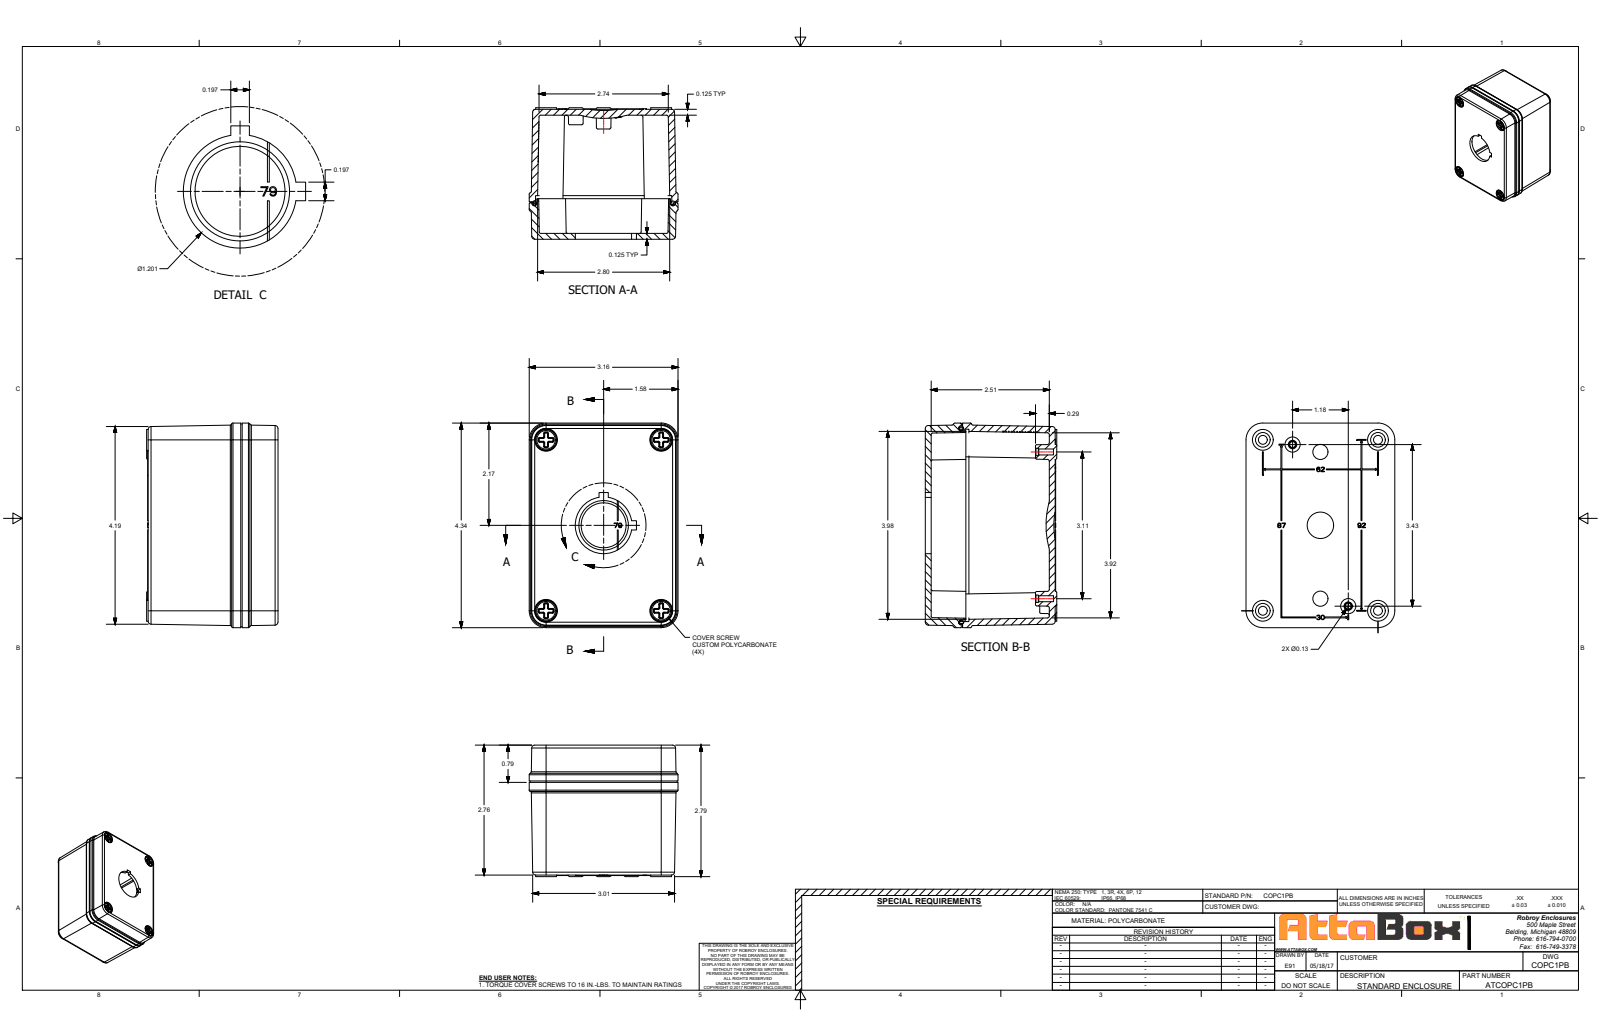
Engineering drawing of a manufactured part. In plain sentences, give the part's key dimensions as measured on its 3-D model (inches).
The part is named "COPC1PB". Its 3-D file was written by "SolidWorks 2018 (AUTOMOTIVE_DESIGN)". It is 7 solids with 1106 faces: 259 planar, 474 cylindrical and 373 other. Overall it measures 4.336 by 3.155 by 2.787 inches. Its volume is 9.941 cubic inches and its surface area 151.5 square inches. Round holes: 6 of diameter 0.1, 4 of diameter 0.187, 4 of diameter 0.312, 4 of diameter 0.46, 2 of diameter 0.126, 2 of diameter 0.146, 2 of diameter 0.157, 2 of diameter 0.495, 2 of diameter 0.495, 1 of diameter 1.201. Round bosses or shafts: 4 of diameter 0.44, 4 of diameter 0.433, 4 of diameter 0.276, 2 of diameter 0.309, 2 of diameter 0.306, 2 of diameter 0.1. Partial cylindrical surfaces (rounded edges, fillets, slot ends): 48 of radius 0.01, 48 of radius 0.02, 16 of radius 0.03, 15 of radius 0.02, 12 of radius 0.015, 8 of radius 0.033, 8 of radius 0.07, 8 of radius 0.12. The main face-to-face distances are 0.125, 2.755, 2.63, 2.63, 2.505, 0.125, 0.161, 2.8, 0.178, 1.965. The hole center spacings are 1.247, 2.184, 3.581, 0.57, 0.611, 0.637, 1.555, 1.811.
